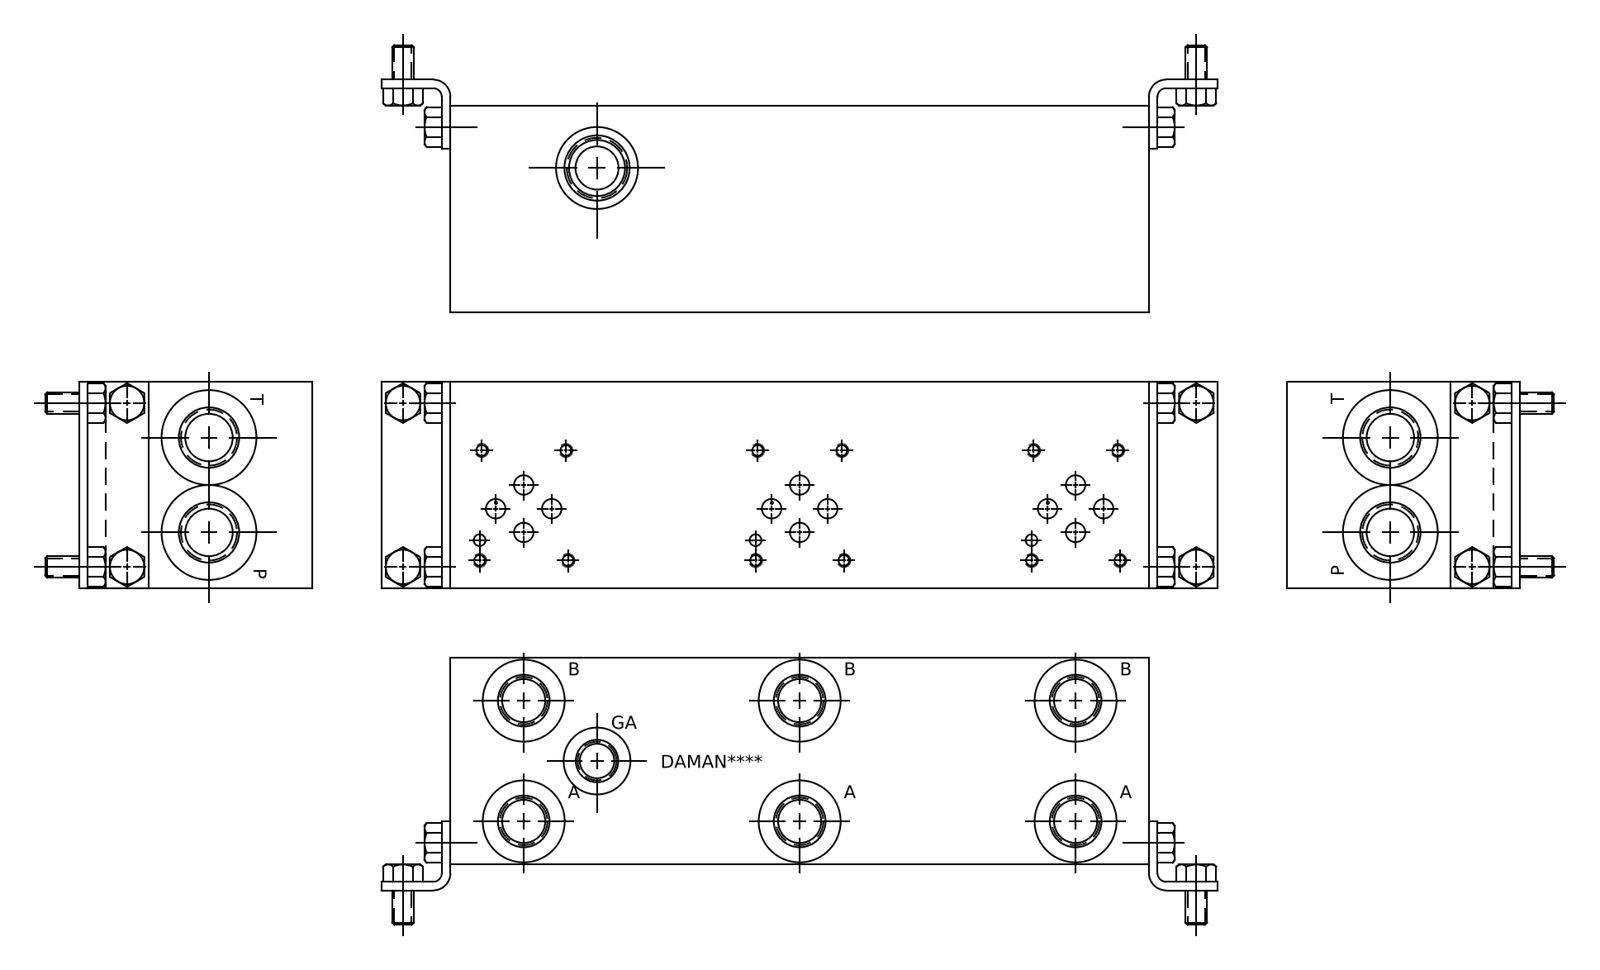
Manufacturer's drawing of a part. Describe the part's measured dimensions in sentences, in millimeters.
The part is named "D03P034S_C". Its 3-D file was written by "Autodesk Inventor 2021 (AUTOMOTIVE_DESIGN)". It is 1 solid with 807 faces: 411 planar, 118 cylindrical and 278 other. Overall it measures 257.18 by 76.2 by 76.2 millimeters. Its volume is 1 381 000 cubic millimeters and its surface area 115 726 square millimeters. Round holes: 12 of diameter 3.78, 12 of diameter 4.83, 9 of diameter 7.14, 7 of diameter 17.5, 7 of diameter 19.05, 7 of diameter 19.25, 6 of diameter 14.3, 6 of diameter 30.63, 3 of diameter 3.96, 3 of diameter 6.35, 3 of diameter 15.88, 2 of diameter 6.53. Partial cylindrical surfaces (rounded edges, fillets, slot ends): 1 of radius 5.25, 1 of radius 6.15. The main face-to-face distances are 76.2, 0.79, 257.18, 75.41, 256.39, 255.6, 61.14, 15.06, 14.27, 74.62. The hole center spacings are 101.6, 203.2, 19.95, 22.05, 33.55, 40.49, 51.45, 80.73.
